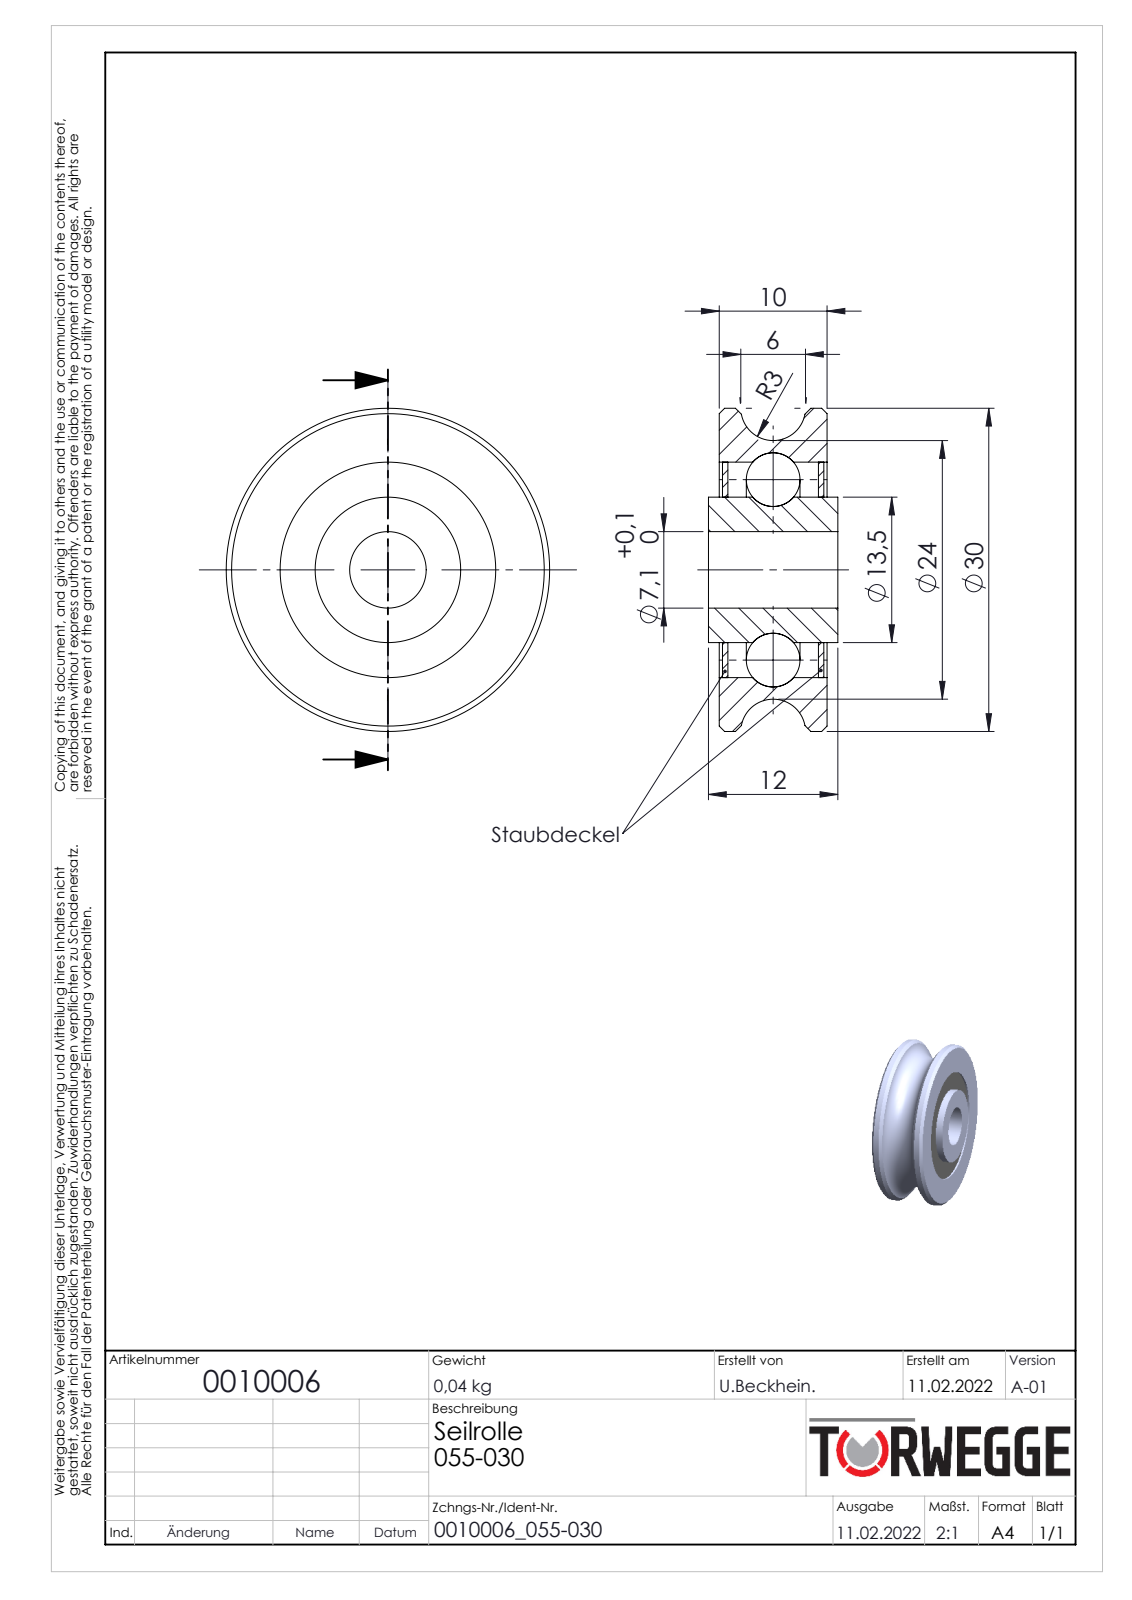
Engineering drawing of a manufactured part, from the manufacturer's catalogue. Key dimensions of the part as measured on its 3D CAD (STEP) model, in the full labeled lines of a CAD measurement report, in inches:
Part name (STEP PRODUCT): 0010006
STEP written by: SolidWorks 2020 (AUTOMOTIVE_DESIGN)
Units: inches
Bodies: 5 solids, 50 faces (8 planar, 22 cylindrical, 20 other)
Overall size (bounding box): 1.181 × 1.181 × 0.472
Volume: 0.296 in³ · Surface area: 7.917 in²
Round holes (diameter × count): ⌀0.28 ×1, ⌀0.531 ×1, ⌀0.787 ×1
Round bosses / shafts (diameter × count): ⌀1.181 ×1
Main face-to-face distances: 0.394, 0.031, 0.362, 0.382, 0.02, 0.35, 0.039, 0.051, 0.071, 0.402
